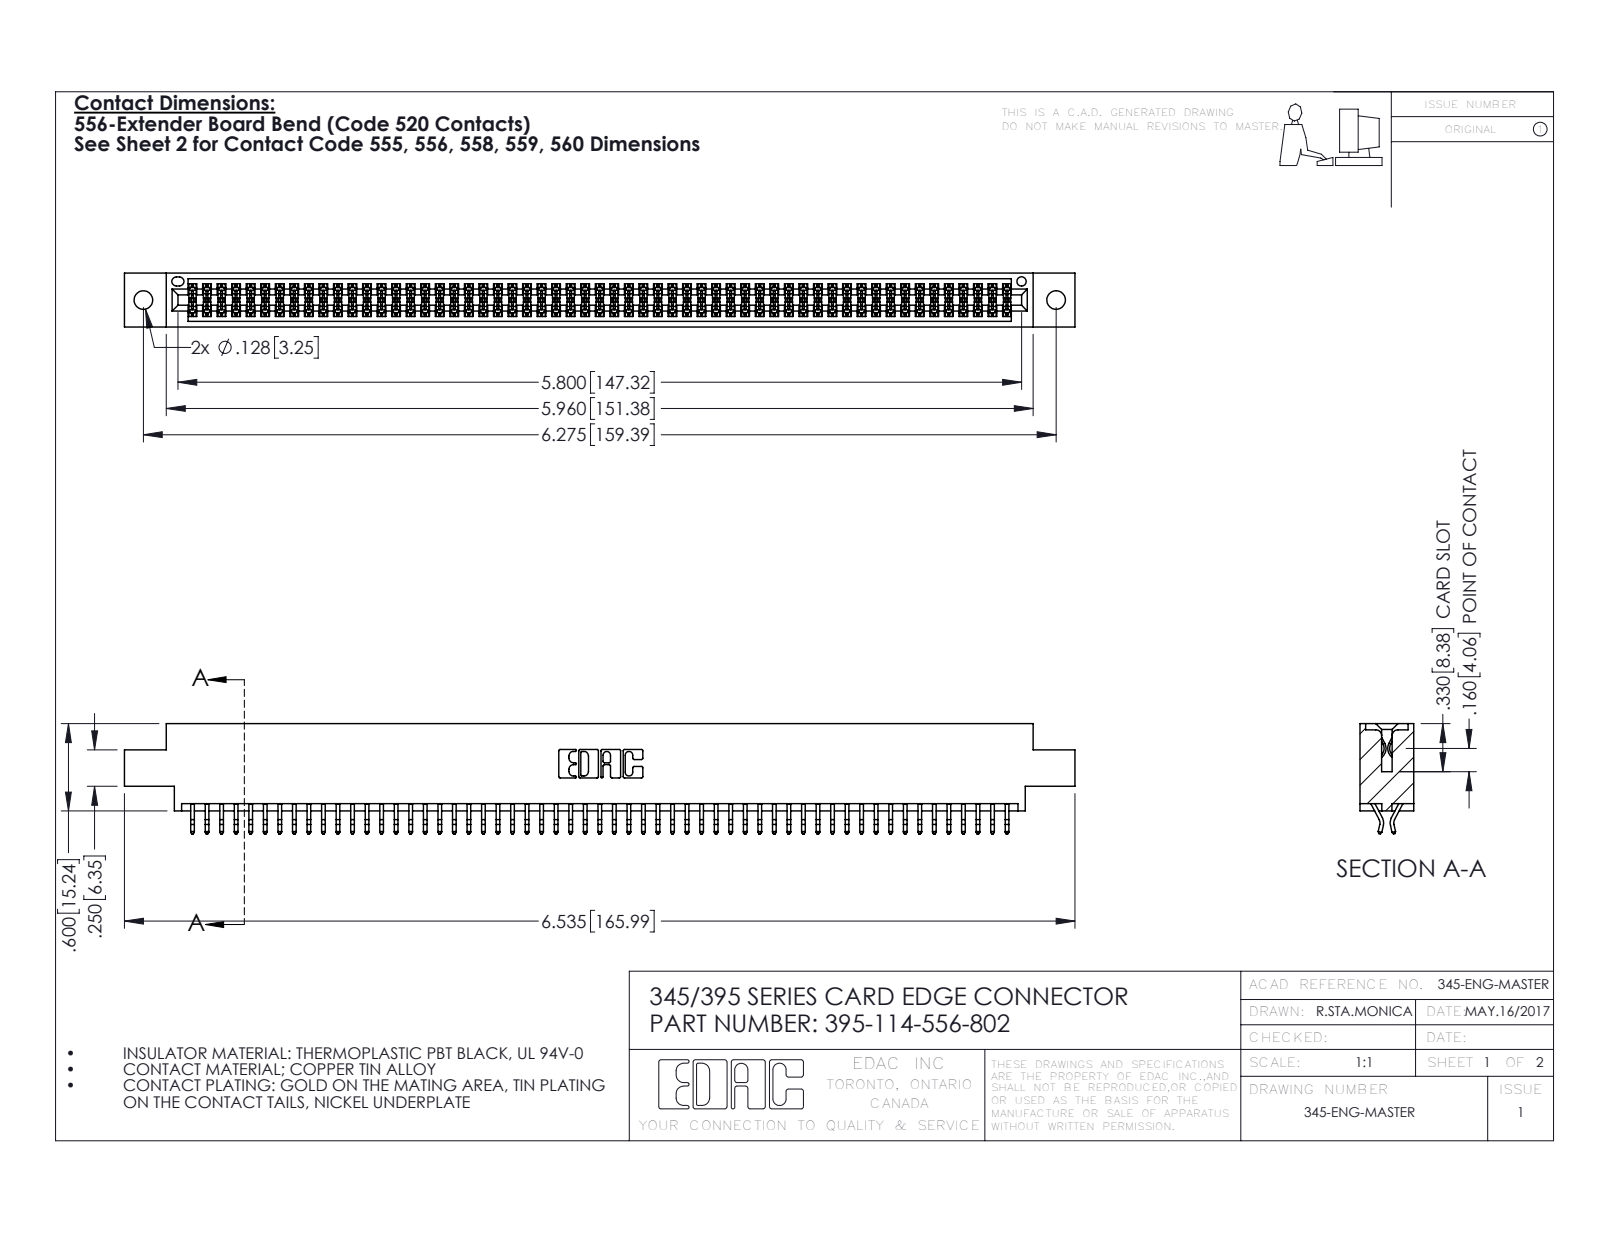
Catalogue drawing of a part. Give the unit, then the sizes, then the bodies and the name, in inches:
Units: inches
Overall size (bounding box): 6.535 × 0.757 × 0.37
Round holes (diameter × count): ⌀0.128 ×2, ⌀0.064 ×1
Partial cylindrical surfaces — rounded edges, fillets, slot ends (radius × count): R0.006 ×171, R0.01 ×22, R0.007 ×6, R0.031 ×6, R0.026 ×3, R0.01 ×2, R0.014 ×2, R0.019 ×2
Main face-to-face distances: 0.298, 0.072, 0.37, 0.025, 0.2, 0.098, 0.272, 0.225, 0.175, 0.149
Hole centre spacings: 0.27, 6.039, 6.275
Volume: 0.983 in³ · Surface area: 37 in²
Bodies: 115 solids, 6514 faces (4302 planar, 2212 cylindrical, 0 other)
Part name (STEP PRODUCT): 395-114-556-802; 345 Part_0.170 Offset - 0.128 Dia; 345-292-001_556 Tail
STEP written by: SolidWorks 2016 (CONFIG_CONTROL_DESIGN)
